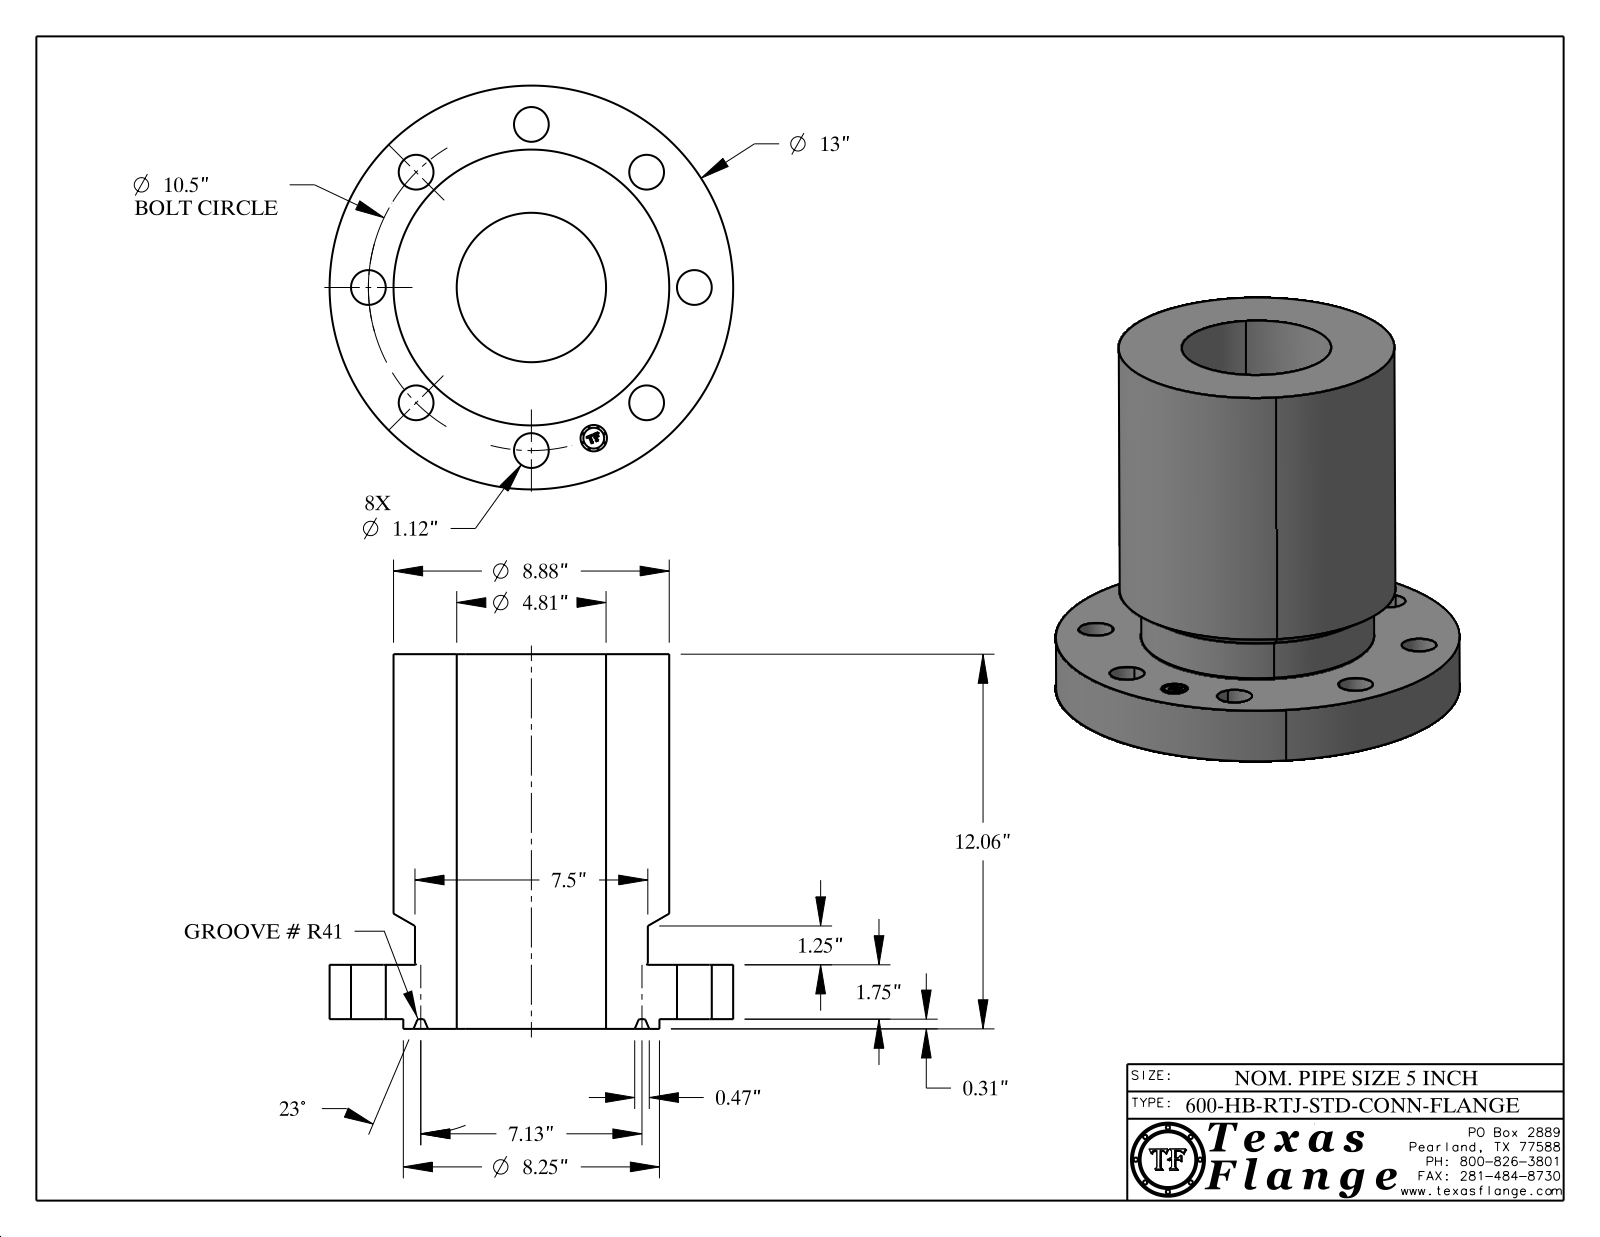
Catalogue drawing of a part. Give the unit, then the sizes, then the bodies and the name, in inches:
Units: inches
Overall size (bounding box): 13 × 13 × 12.063
Round holes (diameter × count): ⌀1.12 ×8, ⌀0.85 ×1, ⌀4.81 ×1
Round bosses / shafts (diameter × count): ⌀0.051 ×8, ⌀13 ×1, ⌀8.88 ×1, ⌀8.25 ×1, ⌀7.5 ×1, ⌀0.67 ×1
Main face-to-face distances: 1.75, 11.75, 10, 0.313, 2.063, 12.063, 2.058, 1.745, 10.005, 0.254
Hole centre spacings: 5.25, 4.018, 9.701, 7.424, 7.425, 2.048, 5.833, 8.73
Volume: 607.1 in³ · Surface area: 835.2 in²
Bodies: 1 solid, 431 faces (371 planar, 46 cylindrical, 14 other)
Part name (STEP PRODUCT): 5-600-HB-RTJ-STD-CONN-FLANGE
STEP written by: CATIA V5 STEP AP214 (AUTOMOTIVE_DESIGN)
